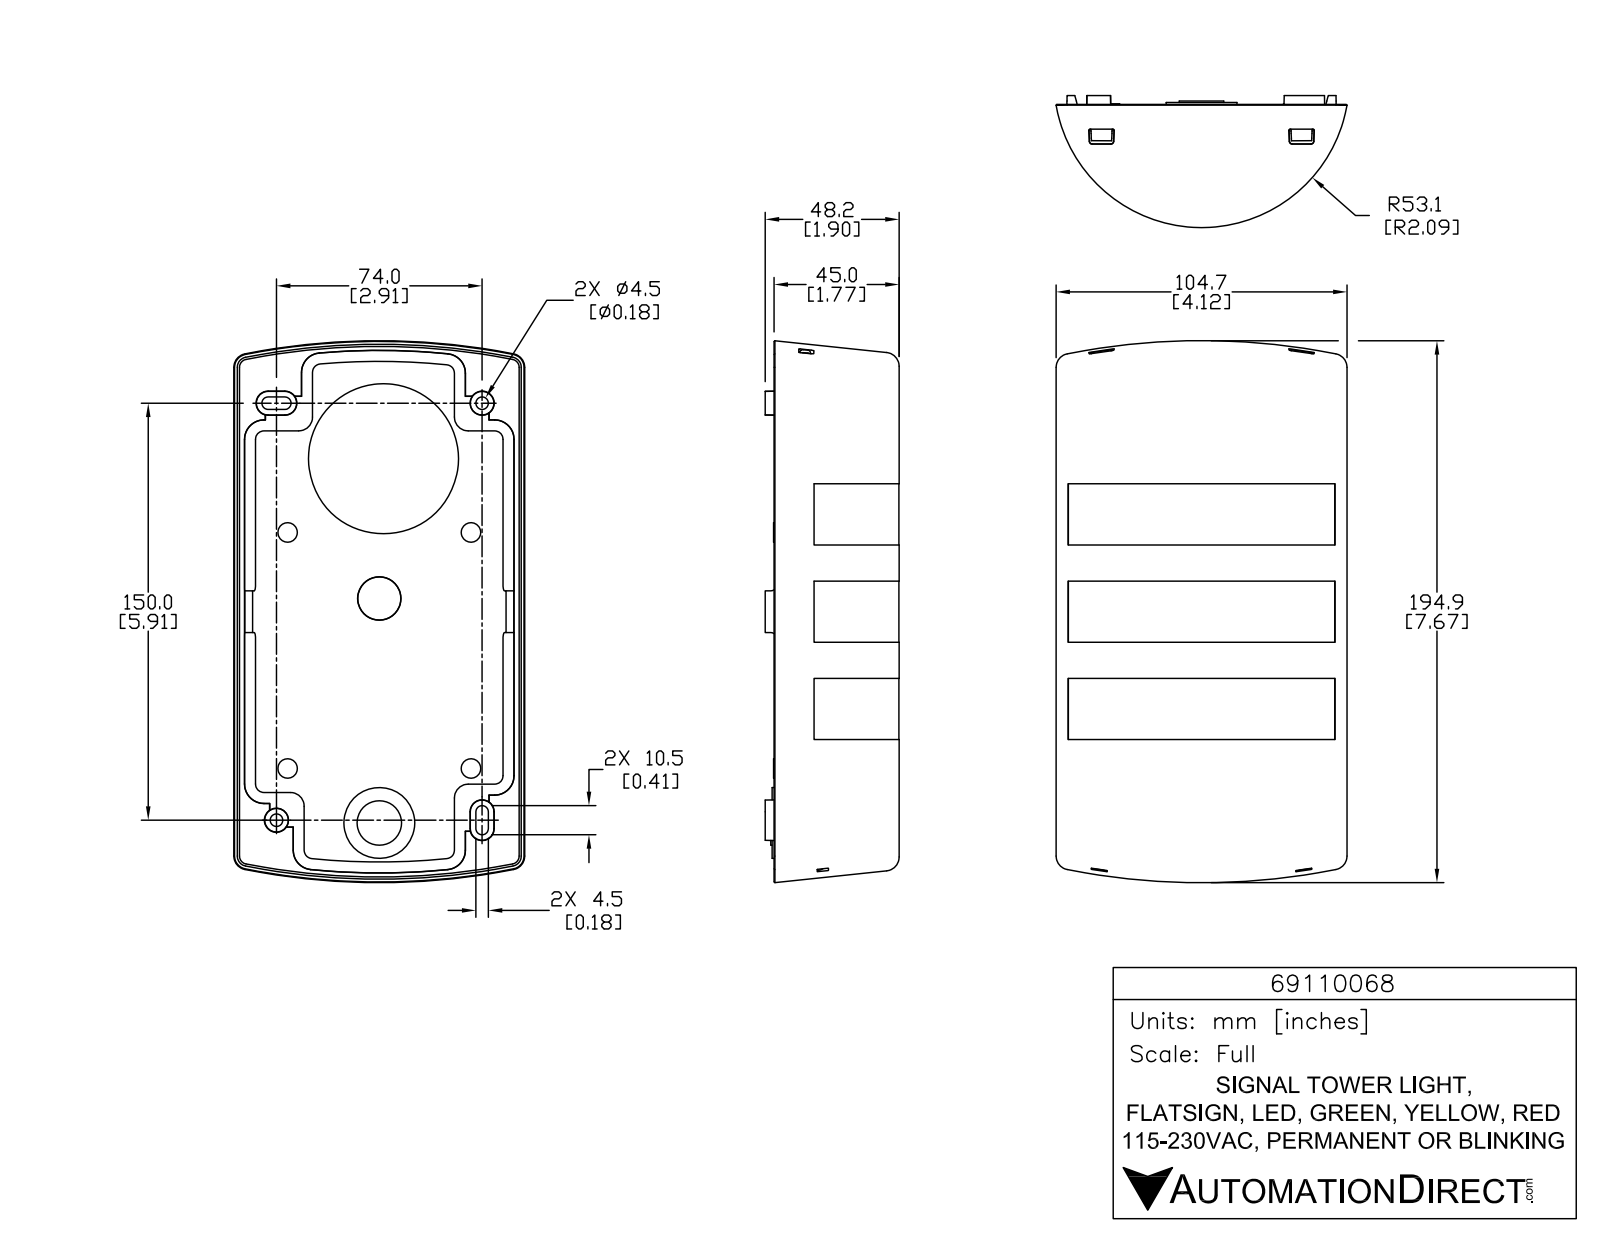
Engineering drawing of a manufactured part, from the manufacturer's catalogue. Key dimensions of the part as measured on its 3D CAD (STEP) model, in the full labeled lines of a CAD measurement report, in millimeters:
Part name (STEP PRODUCT): 69110068
STEP written by: SolidWorks 2017 (AUTOMOTIVE_DESIGN)
Units: millimetres
Bodies: 1 solid, 1074 faces (520 planar, 128 cylindrical, 426 other)
Overall size (bounding box): 194.9 × 104.7 × 48.3
Volume: 628 600 mm³ · Surface area: 59 790 mm²
Round holes (diameter × count): ⌀2.3 ×1
Round bosses / shafts (diameter × count): ⌀54 ×1, ⌀25.5 ×1, ⌀16 ×1, ⌀13.1 ×1, ⌀3.3 ×1
Partial cylindrical surfaces — rounded edges, fillets, slot ends (radius × count): R1 ×12, R0.3 ×4, R0.2 ×3, R0.2 ×2, R0.5 ×2, R0.5 ×2, R0.5 ×2, R0.5 ×2
Main face-to-face distances: 0.8, 2, 1.2, 2.8, 1.6, 4, 1, 0.5, 3.5, 3
